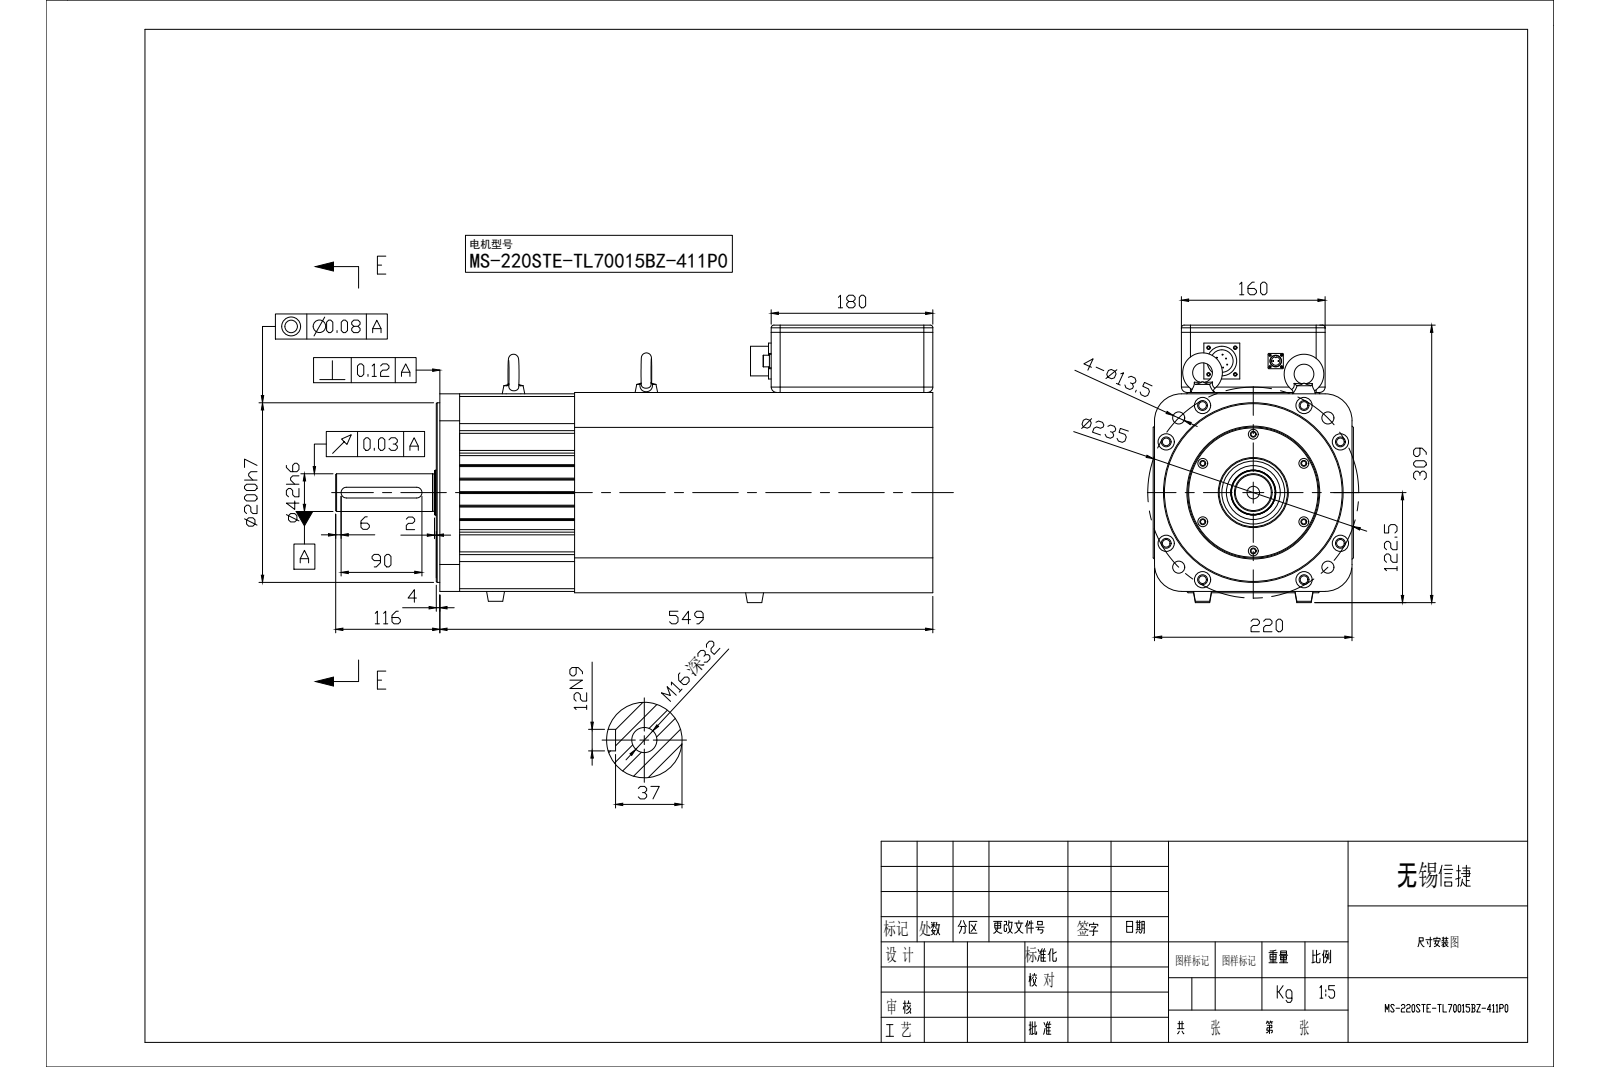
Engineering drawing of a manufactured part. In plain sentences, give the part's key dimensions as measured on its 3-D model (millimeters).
The part is named "MS-220STE-TL70015BZ-411P0-S01". Its 3-D file was written by "SolidWorks 2016 (CONFIG_CONTROL_DESIGN)". It is 0 solids with 543 faces: 200 planar, 269 cylindrical and 74 other. Overall it measures 665 by 309 by 223 millimeters. Round holes: 8 of diameter 18, 6 of diameter 4.2, 6 of diameter 11, 4 of diameter 4, 4 of diameter 6, 4 of diameter 6.6, 4 of diameter 12, 4 of diameter 13.5, 3 of diameter 2.5, 1 of diameter 9.5, 1 of diameter 14, 1 of diameter 17. Round bosses or shafts: 8 of diameter 1, 2 of diameter 14, 2 of diameter 12, 1 of diameter 200, 1 of diameter 76, 1 of diameter 60, 1 of diameter 49.8, 1 of diameter 42. Partial cylindrical surfaces (rounded edges, fillets, slot ends): 42 of radius 1, 20 of radius 3, 12 of radius 108.67, 6 of radius 6, 4 of radius 10, 4 of radius 30, 4 of radius 110.67, 1 of radius 103.25. The main face-to-face distances are 1.5, 221.5, 220, 223, 258.84, 180.5, 42.5, 41, 179, 15.02. The hole center spacings are 65, 30.01, 38.37, 112.26, 121.39, 140.28, 143.86, 155.71.
